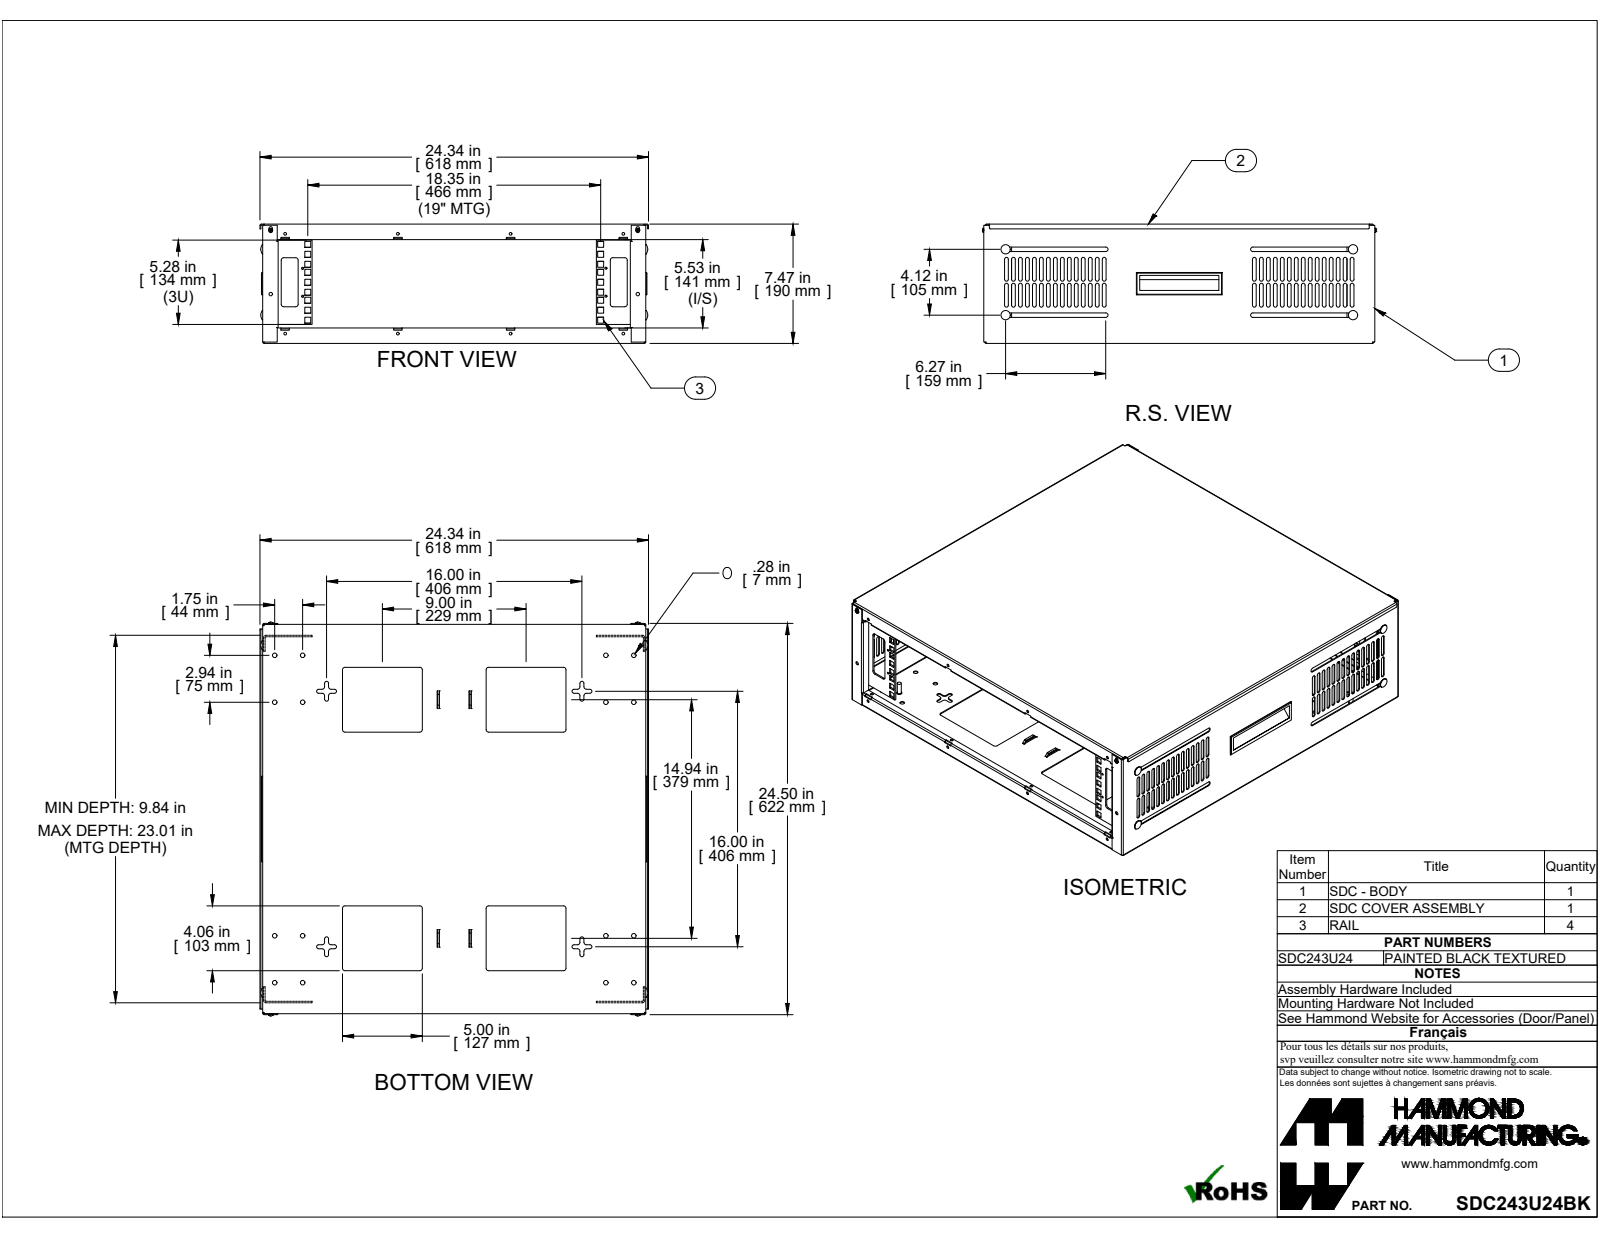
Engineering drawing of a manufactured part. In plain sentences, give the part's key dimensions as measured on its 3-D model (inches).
The part is named "SDC243U24BK". Its 3-D file was written by "SolidWorks 2019 (CONFIG_CONTROL_DESIGN)". It is 36 solids with 1890 faces: 1198 planar, 640 cylindrical and 52 other. Overall it measures 24.67 by 24.344 by 7.472 inches. Its volume is 103.4 cubic inches and its surface area 3 534 square inches. Round holes: 16 of diameter 0.17, 16 of diameter 0.281, 8 of diameter 0.125, 4 of diameter 0.196, 2 of diameter 0.159, 2 of diameter 0.187, 2 of diameter 0.213. Round bosses or shafts: 8 of diameter 0.25, 4 of diameter 0.58, 2 of diameter 0.313, 2 of diameter 0.28, 2 of diameter 0.187, 2 of diameter 0.138. Partial cylindrical surfaces (rounded edges, fillets, slot ends): 120 of radius 0.118, 44 of radius 0.157, 22 of radius 0.029, 22 of radius 0.086, 18 of radius 0.117, 16 of radius 0.025, 16 of radius 0.125, 8 of radius 0.03. The main face-to-face distances are 0.057, 7.415, 7.358, 7.472, 23.943, 23.886, 24, 0.072, 0.912, 7.343. The hole center spacings are 1.75, 2.937, 3.419, 7.063, 17.563, 17.65, 19.005, 19.085.
